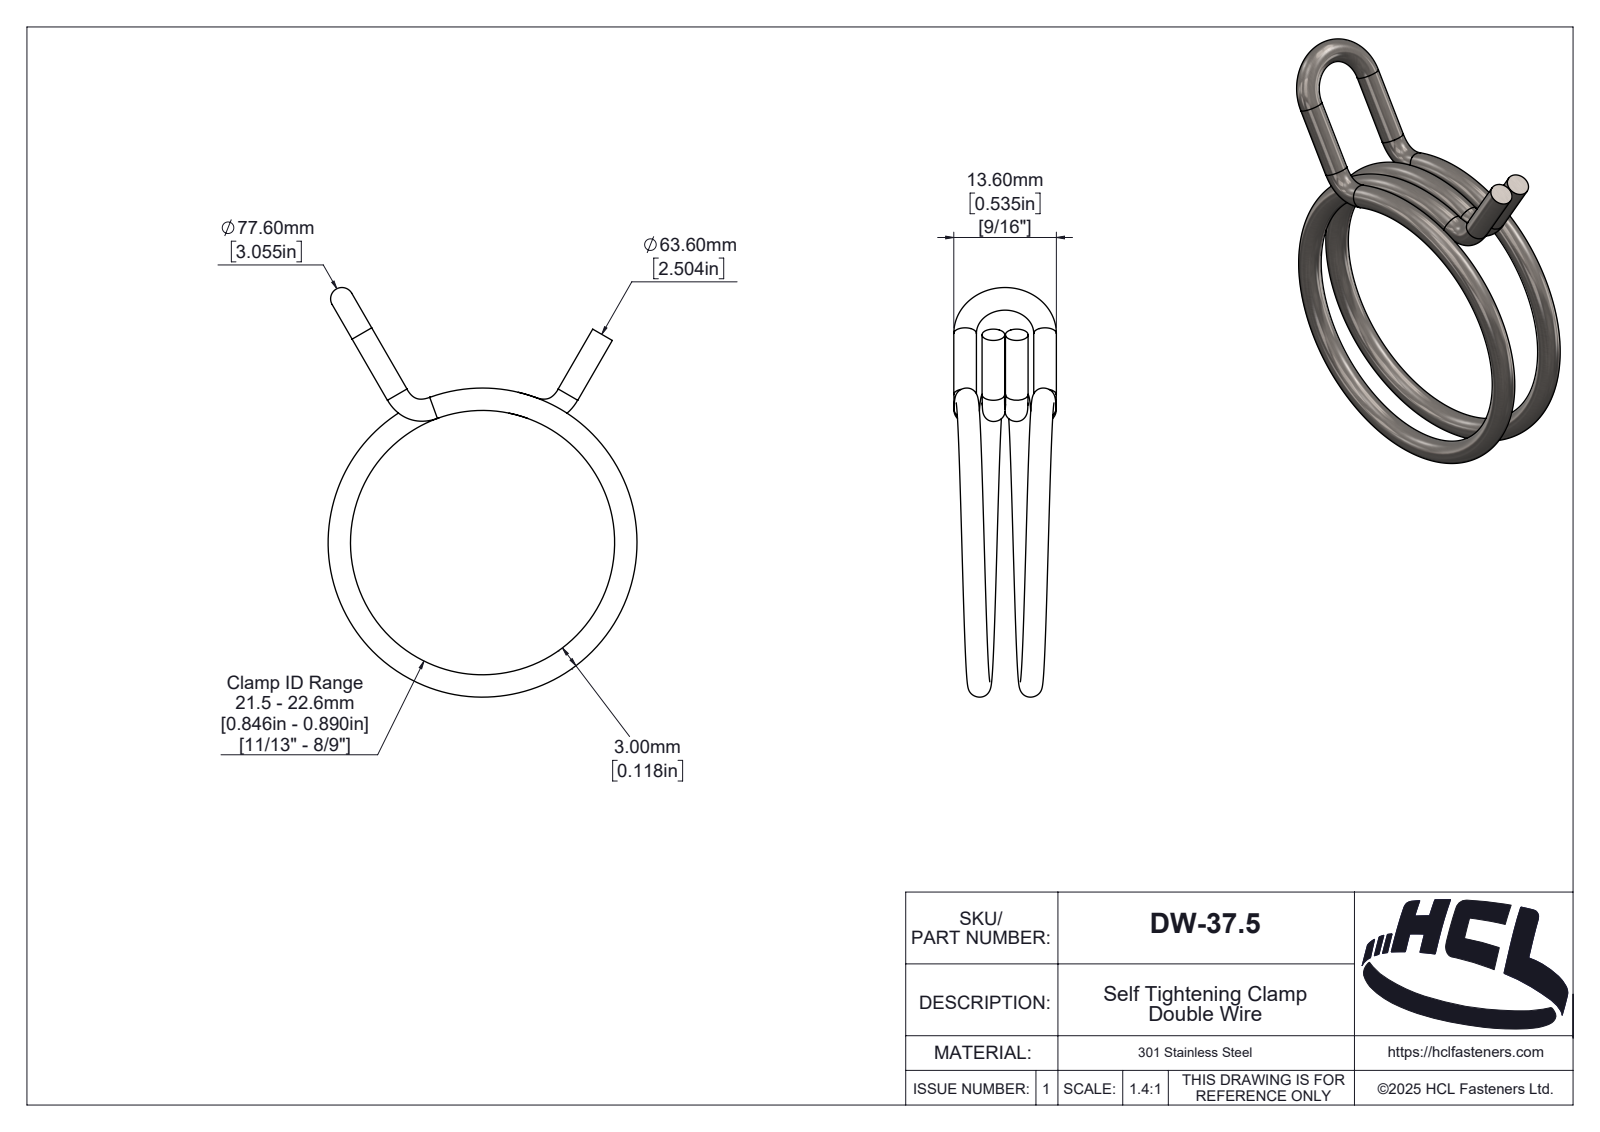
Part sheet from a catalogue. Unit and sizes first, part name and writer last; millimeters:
Units: millimetres
Overall size (bounding box): 54.28 × 40.95 × 13.6
Round bosses / shafts (diameter × count): ⌀3 ×4
Partial cylindrical surfaces — rounded edges, fillets, slot ends (radius × count): R0.16 ×1, R0.2 ×1, R0.21 ×1, R0.26 ×1, R0.36 ×1, R0.48 ×1, R0.6 ×1, R0.68 ×1
Volume: 2 382 mm³ · Surface area: 3 212 mm²
Bodies: 1 solid, 132 faces (14 planar, 53 cylindrical, 65 other)
Part name (STEP PRODUCT): DW-37.5
STEP written by: SolidWorks 2025 (AUTOMOTIVE_DESIGN)
